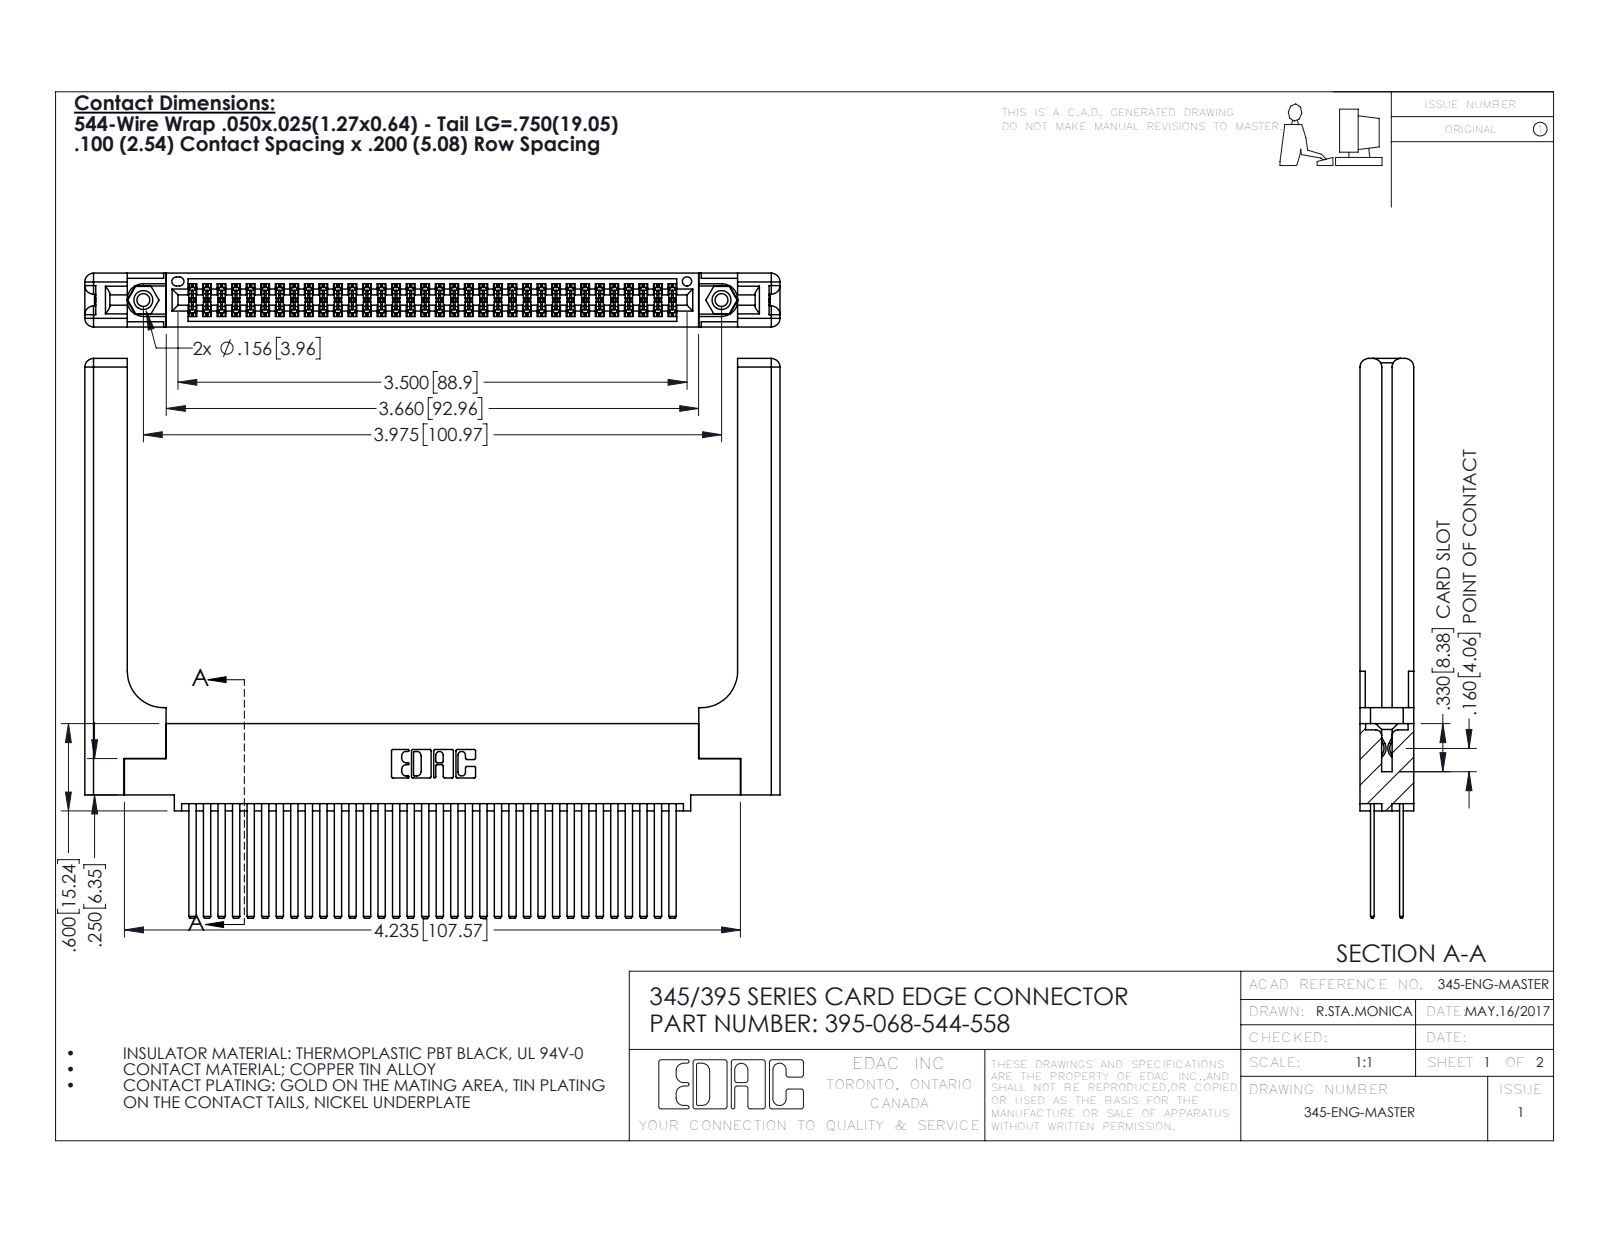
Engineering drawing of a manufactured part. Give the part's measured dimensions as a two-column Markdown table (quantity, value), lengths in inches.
| quantity | value |
| --- | --- |
| part name | 345-250-001_345-250-001-102; 345-220-058_345-220-058; 345-292-001_345-293-144; 345 Part_0.110 Offset - 0.156 Dia-TH (+1 more) |
| STEP written by | SolidWorks 2016 (CONFIG_CONTROL_DESIGN) |
| units | inches |
| bodies | 73 solids, 3378 faces (2204 planar, 1114 cylindrical, 60 other) |
| overall size | 4.779 × 3.847 × 0.37 |
| volume | 1.286 in³ |
| surface area | 40.94 in² |
| round holes (diameter × count) | 0.089 × 2, 0.125 × 2, 0.156 × 2, 0.064 × 1 |
| round bosses / shafts (diameter × count) | 0.155 × 2 |
| partial cylindrical surfaces (radius × count) | 0.006 × 102, 0.01 × 22, 0.06 × 16, 0.007 × 6, 0.031 × 6, 0.026 × 3, 0.014 × 2, 0.019 × 2 |
| main face-to-face distances | 0.072, 0.298, 0.098, 0.272, 0.025, 0.2, 0.37, 0.225, 0.175, 0.148 |
| hole center spacings | 0.27, 3.74, 3.975 |
